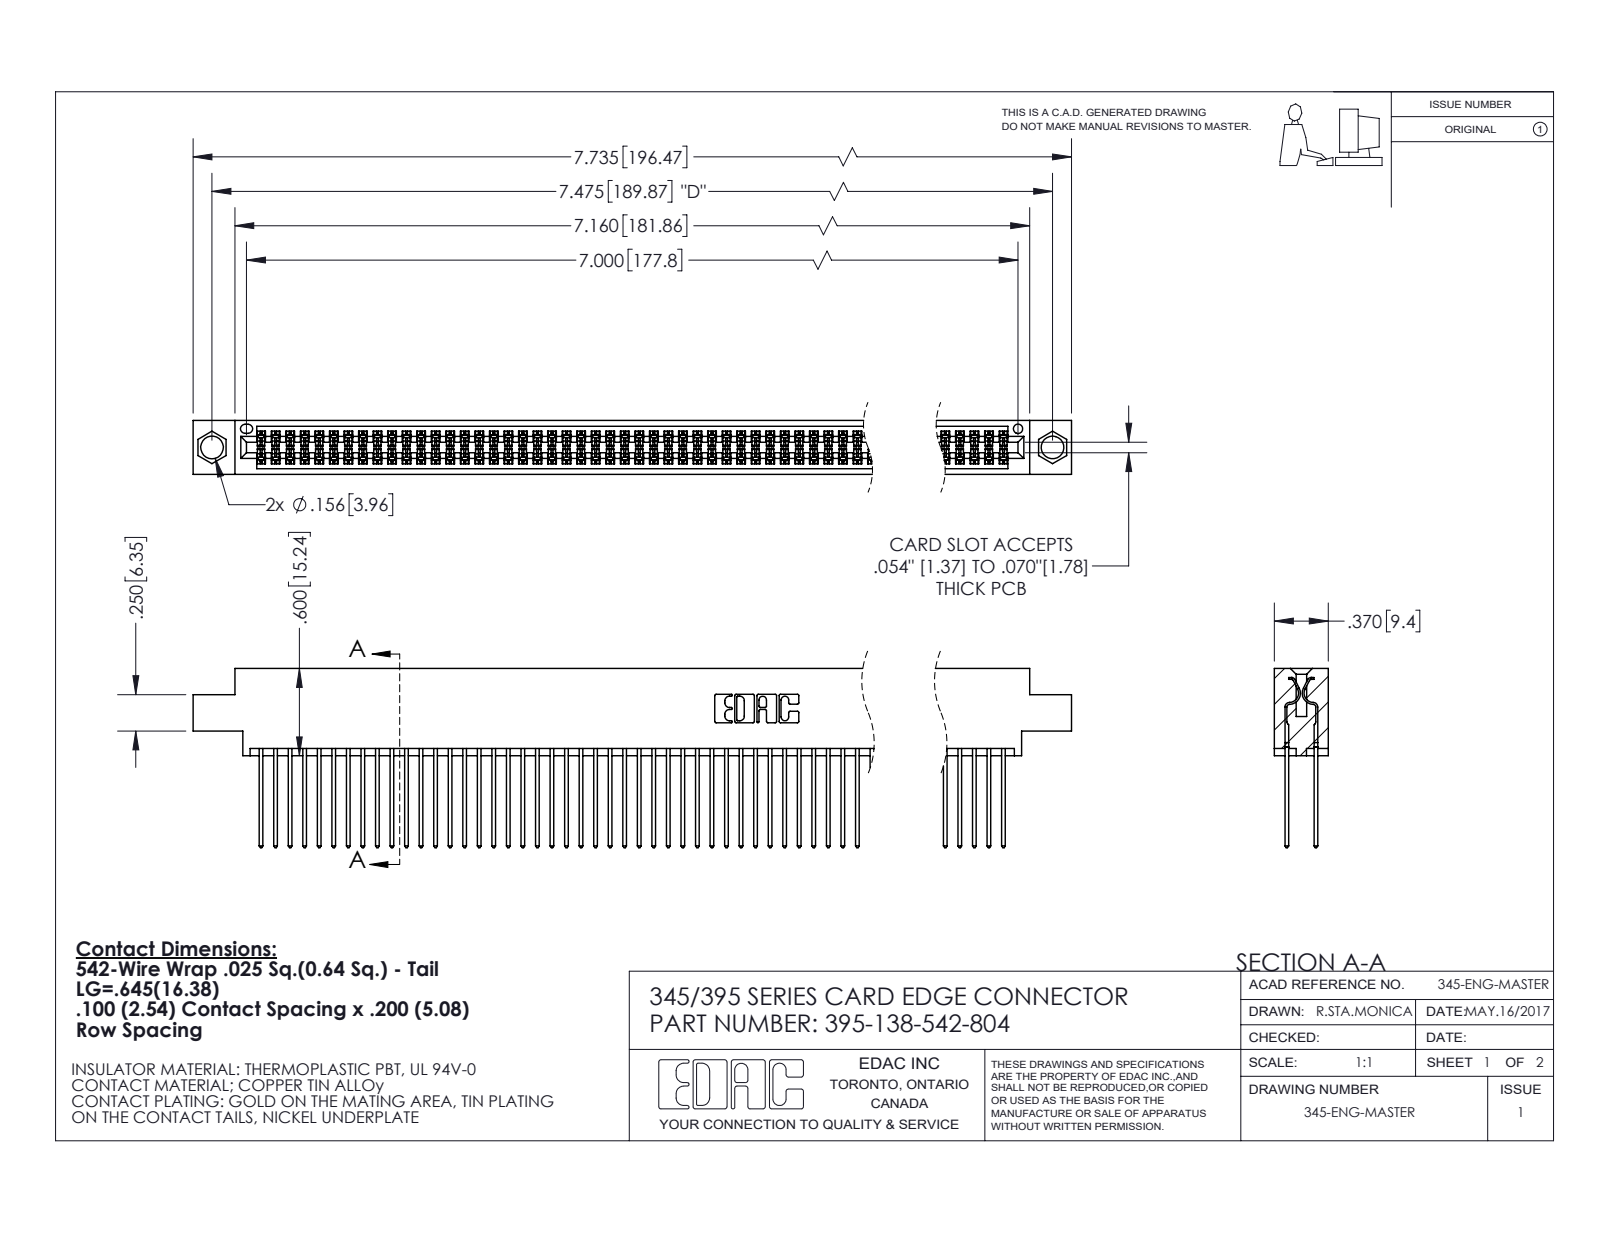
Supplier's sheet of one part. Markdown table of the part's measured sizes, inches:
| quantity | value |
| --- | --- |
| part name | 395-138-542-804; 345 Part_0.170 Offset - 0.156 Dia-TI; 345-292-001_345-293-142 |
| STEP written by | SolidWorks 2020 (CONFIG_CONTROL_DESIGN) |
| units | inches |
| bodies | 139 solids, 7044 faces (4652 planar, 2392 cylindrical, 0 other) |
| overall size | 7.735 × 1.232 × 0.37 |
| volume | 1.206 in³ |
| surface area | 50.74 in² |
| round holes (diameter × count) | 0.156 × 2, 0.064 × 1 |
| partial cylindrical surfaces (radius × count) | 0.006 × 207, 0.01 × 138, 0.01 × 22, 0.007 × 6, 0.031 × 6, 0.026 × 3, 0.014 × 2, 0.019 × 2 |
| main face-to-face distances | 0.072, 0.298, 0.2, 0.098, 0.272, 0.025, 0.225, 0.37, 0.175, 0.149 |
| hole center spacings | 0.27, 7.239, 7.475 |
